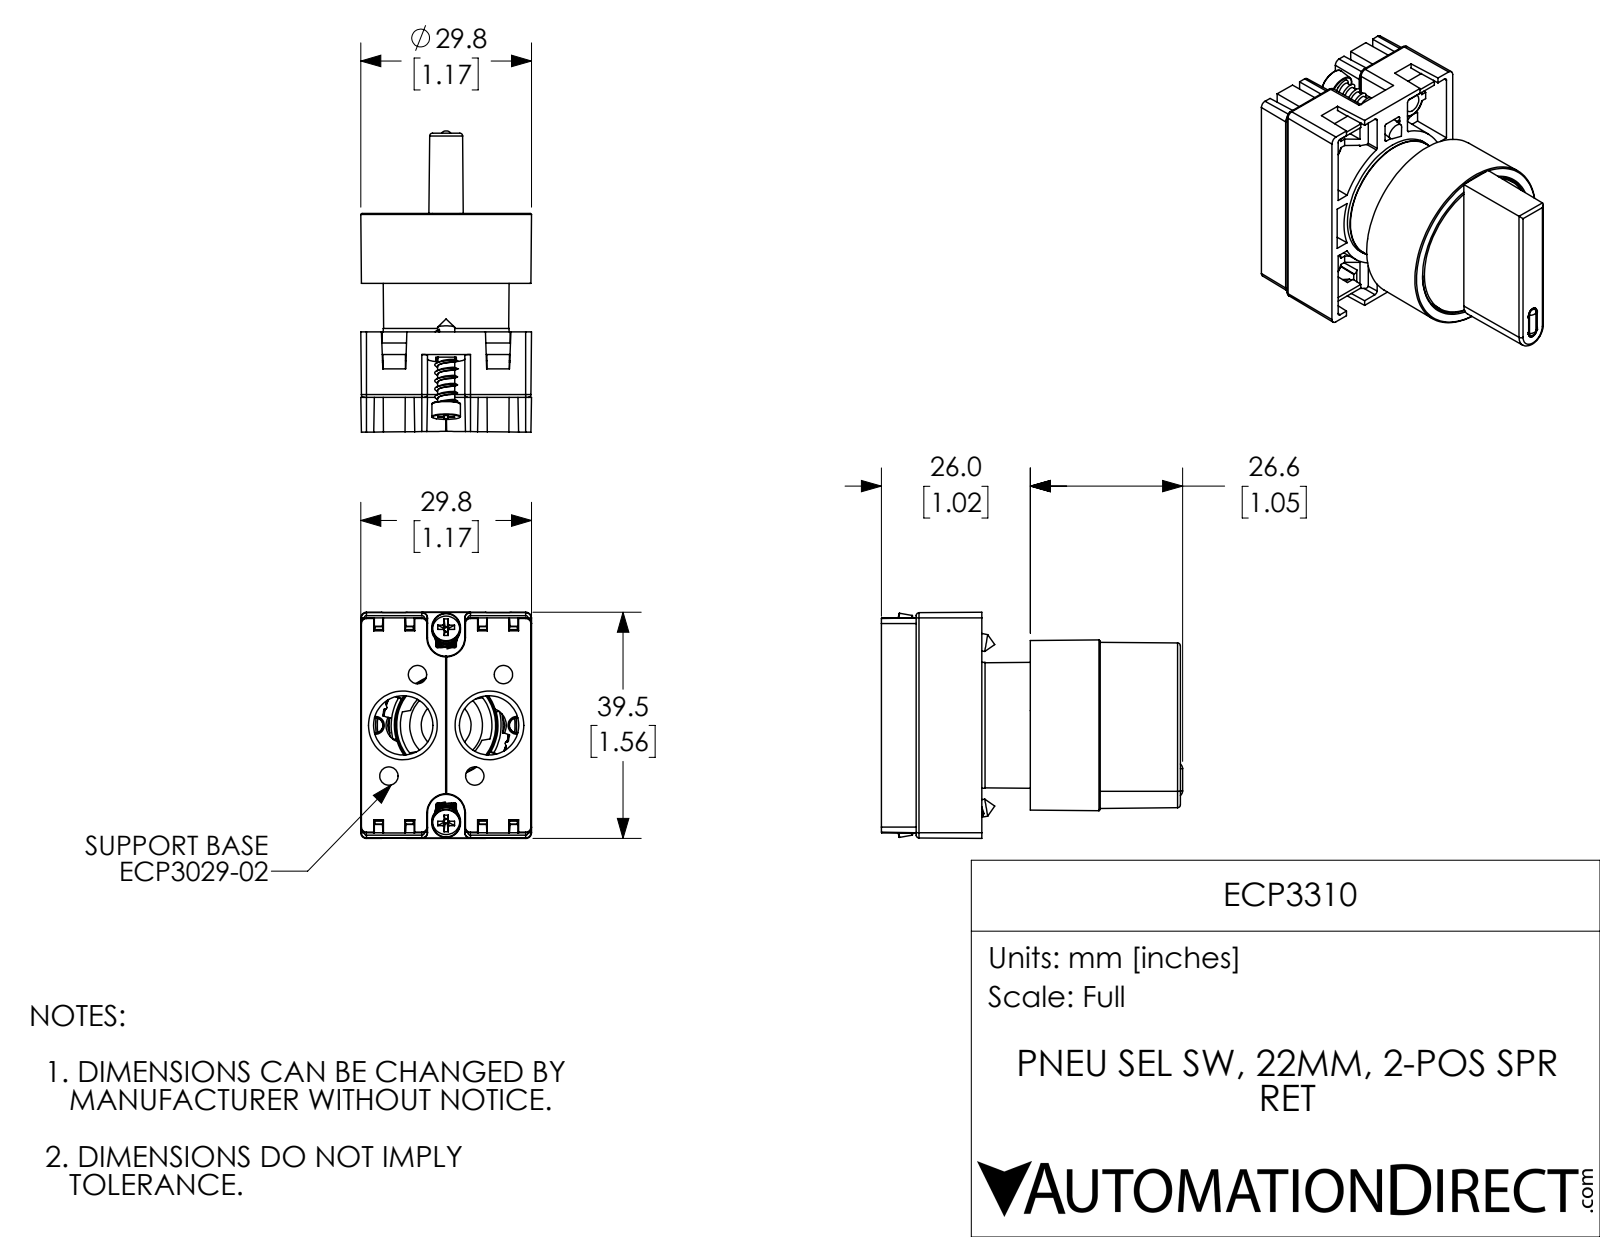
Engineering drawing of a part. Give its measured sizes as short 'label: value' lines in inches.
name: ECP3310
written by: SolidWorks 2017 (AUTOMOTIVE_DESIGN)
unit: in
bodies: 8 solids, 839 faces (404 planar, 157 cylindrical, 278 other)
size: 2.071 × 1.555 × 1.173
volume: 1.095 in³; area: 31.53 in²
holes: 4× ⌀0.081, 2× ⌀0.407, 1× ⌀0.5, 1× ⌀0.551, 1× ⌀0.697, 1× ⌀0.75, 1× ⌀0.756, 1× ⌀0.854, 1× ⌀0.976, 1× ⌀1.024
bosses: 2× ⌀0.197, 2× ⌀0.118, 1× ⌀1.004, 1× ⌀0.866, 1× ⌀0.85, 1× ⌀0.669, 1× ⌀0.343
rounds: 21× R0.02, 10× R0.012, 9× R0.039, 8× R0.006, 4× R0.008, 2× R0.008, 2× R0.118, 2× R0.128
face distances: 1.265, 0.059, 0.067, 0.712, 0.743, 0.299, 0.712, 0.715, 0.814, 0.451
hole spacings: 0.304, 0.541, 0.817, 0.295, 0.472, 0.972, 1.081, 0.591
